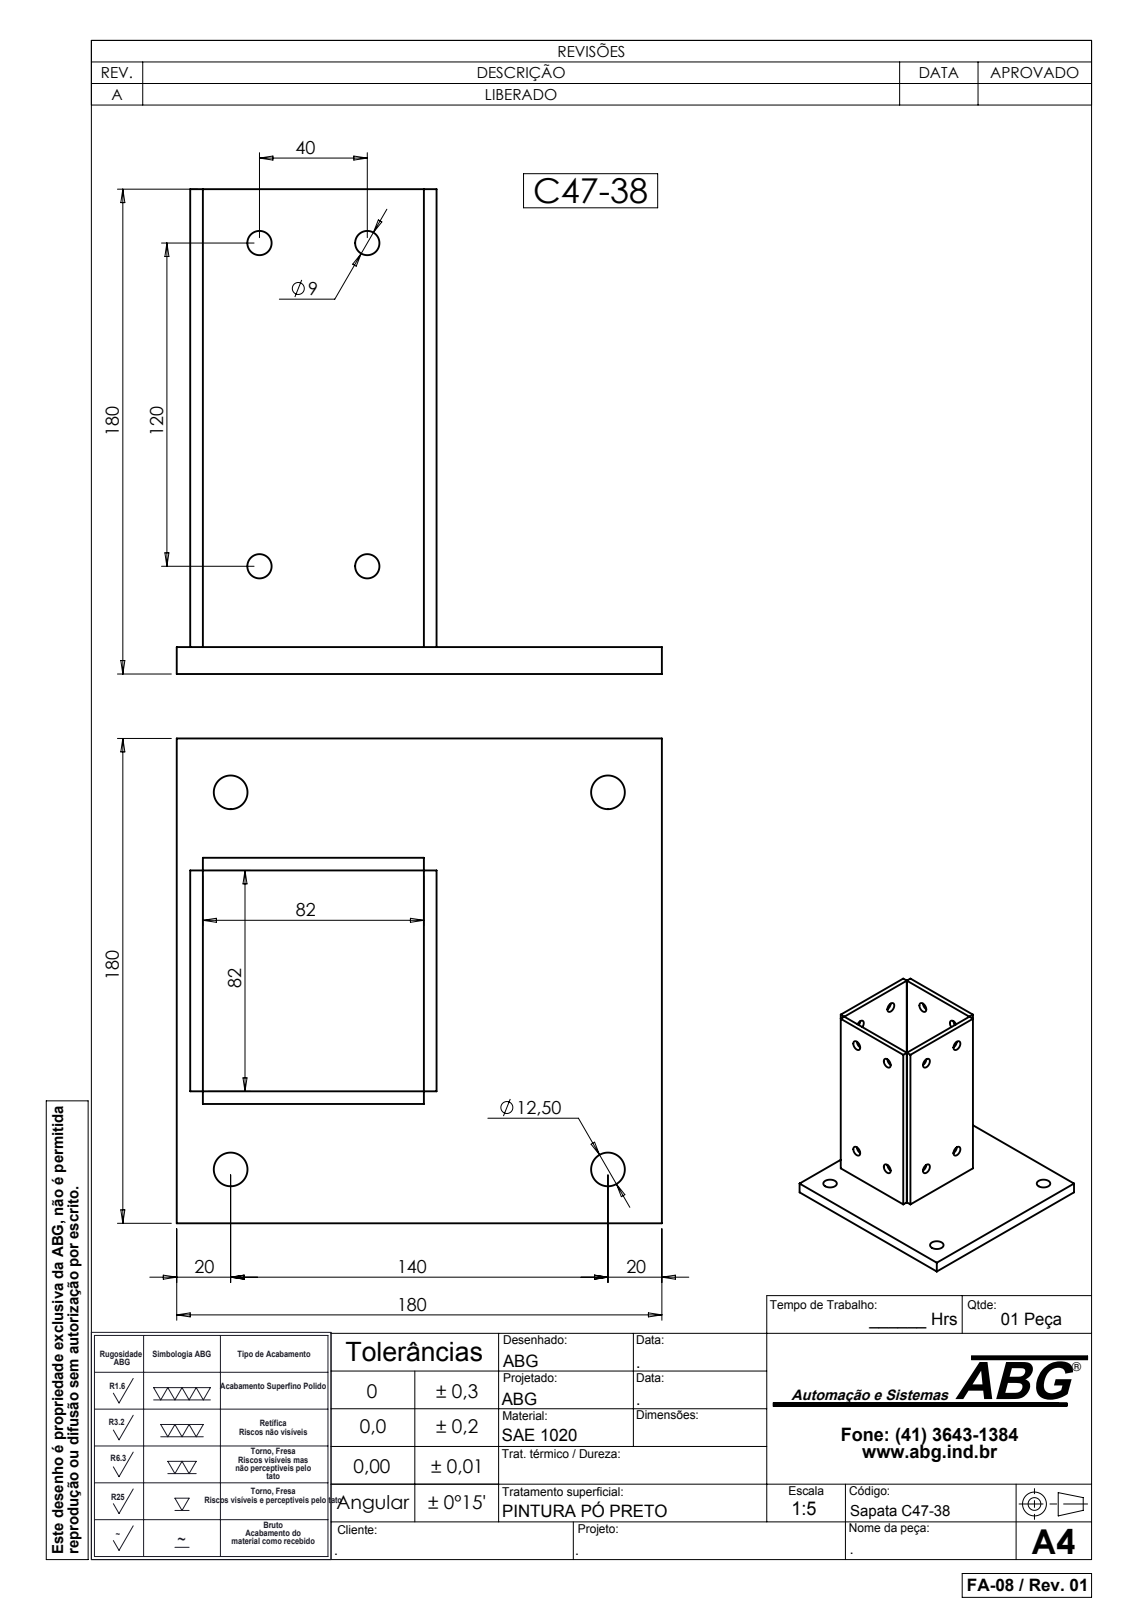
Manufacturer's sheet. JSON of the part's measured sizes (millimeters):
{"part_name": "C47-38; C47-36; Lateral C47-36", "step_written_by": "SolidWorks 2007 (CONFIG_CONTROL_DESIGN)", "units": "millimeters", "bodies": {"solids": 5, "faces": 70, "planar": 30, "cylindrical": 40, "other": 0}, "overall_size": [180, 180, 180], "volume_mm3": 576379, "surface_area_mm2": 193675, "round_holes": [[9, 8], [12.5, 4]], "face_to_face_distances": [4.7, 86.7, 10, 82, 91.4, 180, 44.3, 49, 131, 135.7], "hole_center_spacings": [40, 120, 126.49, 140, 197.99]}
